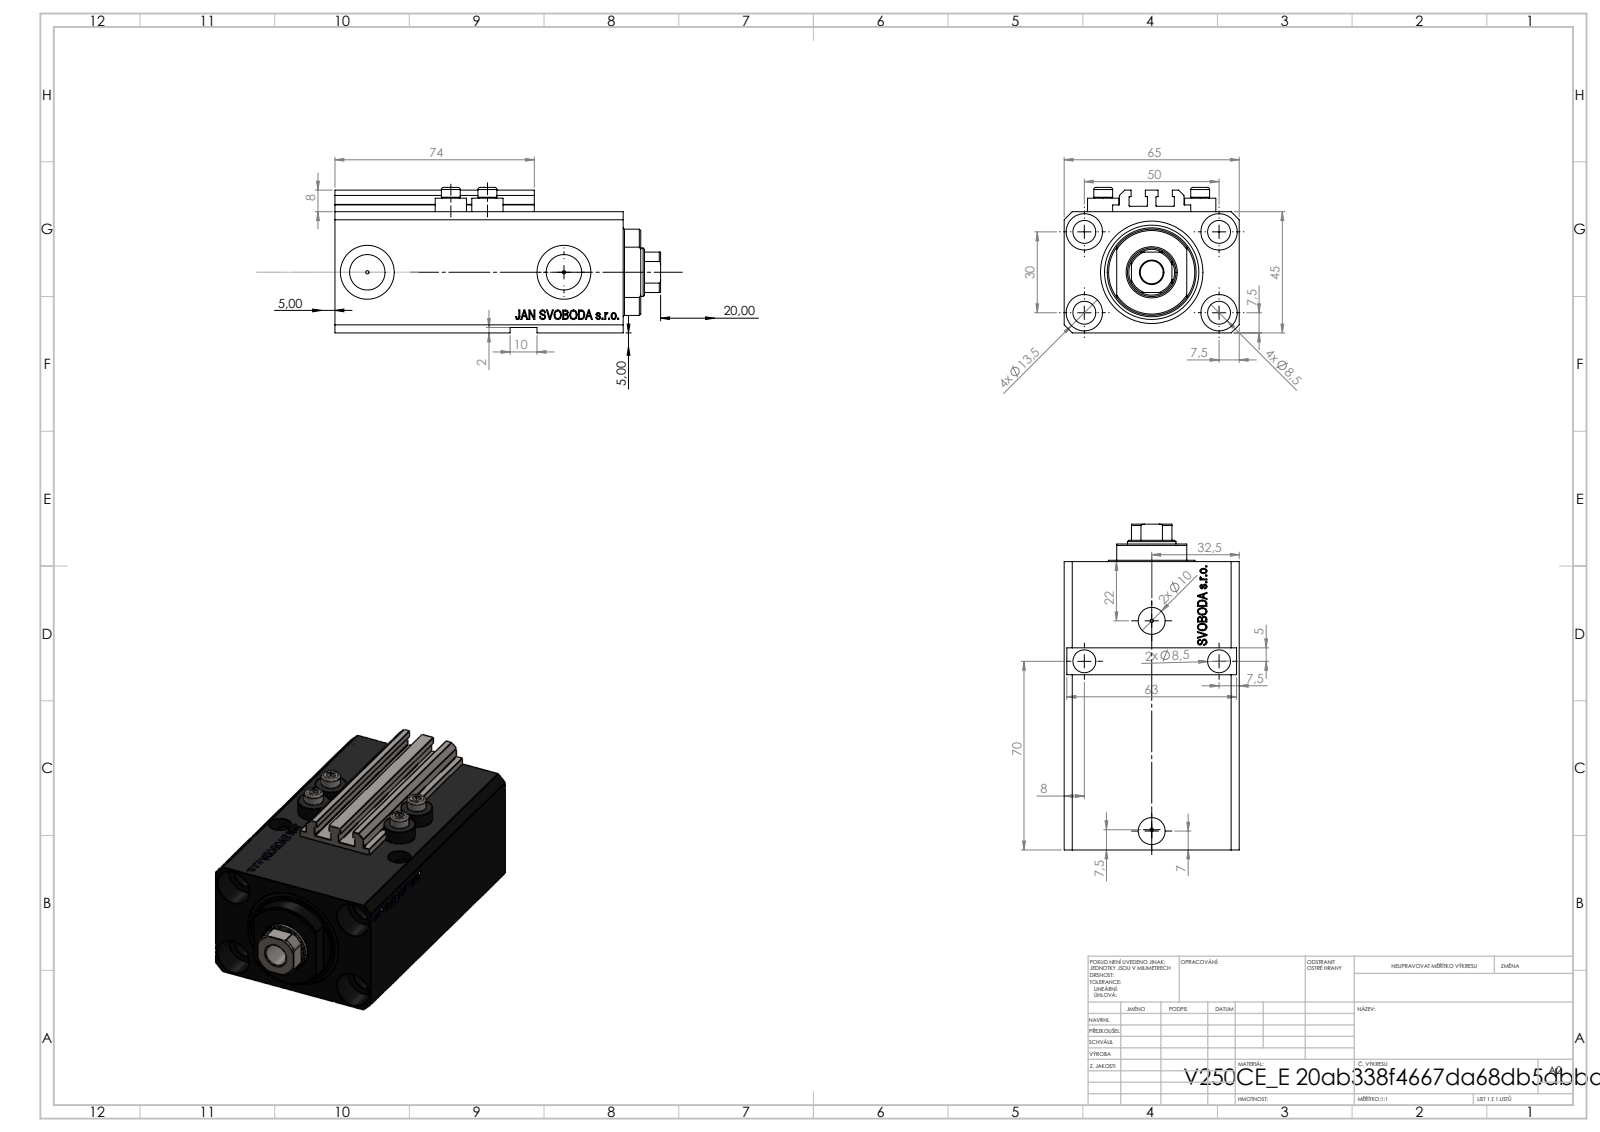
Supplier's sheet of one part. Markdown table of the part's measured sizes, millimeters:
| quantity | value |
| --- | --- |
| part name | ALLEN BOLT V250CE; V250CE_C_VCP; V250CE_VC_E; V250CE_E_Body |
| STEP written by | SolidWorks 2019 (CONFIG_CONTROL_DESIGN) |
| units | millimeters |
| bodies | 8 solids, 1087 faces (511 planar, 146 cylindrical, 430 other) |
| overall size | 121 × 65 × 54 |
| volume | 273 399 mm³ |
| surface area | 76 876 mm² |
| round holes (diameter × count) | 8.5 × 9, 1.25 × 4, 4 × 4, 13.5 × 4, 10 × 2, 13.16 × 2, 20 × 2, 18 × 1, 25 × 1, 38 × 1 |
| round bosses / shafts (diameter × count) | 11.6 × 4, 7 × 4 |
| partial cylindrical surfaces (radius × count) | 0.2 × 10, 8.5 × 1, 16 × 1 |
| main face-to-face distances | 45, 65, 93, 2, 14, 47, 107, 2.5, 10, 20.5 |
| hole center spacings | 29.15, 50, 13.6, 14.76, 15.12, 27.51, 27.89, 30 |
